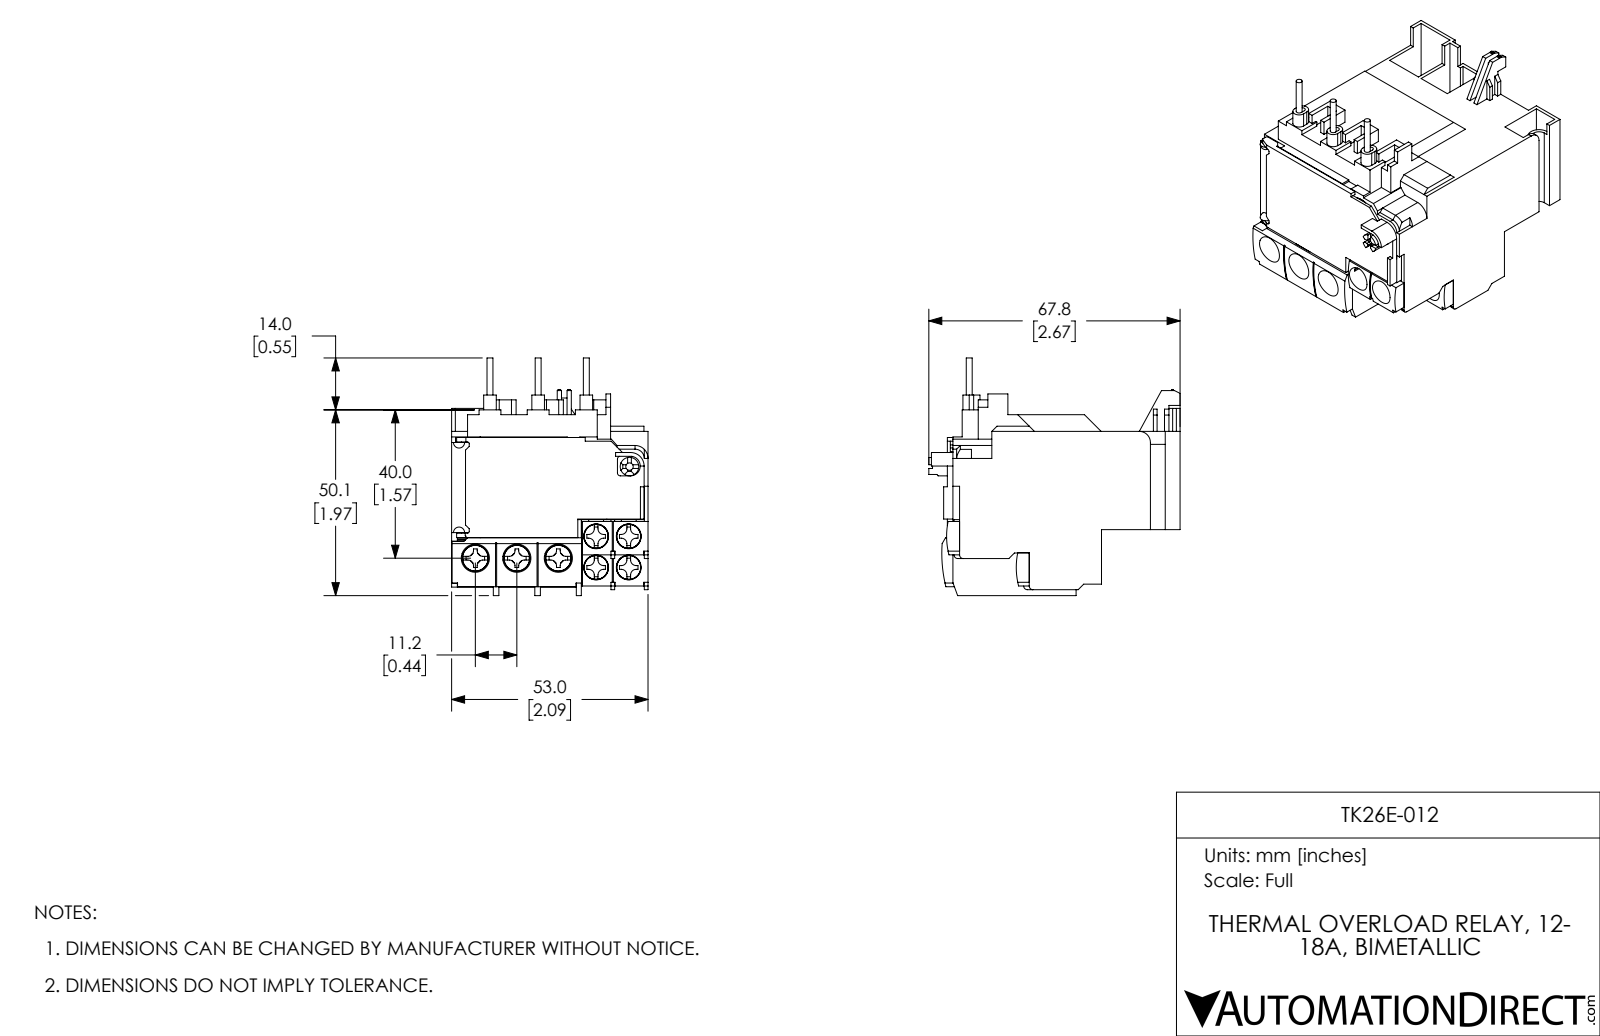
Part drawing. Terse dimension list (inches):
name: TK26E-012
written by: SolidWorks 2017 (AUTOMOTIVE_DESIGN)
unit: in
bodies: 38 solids, 1480 faces (1225 planar, 220 cylindrical, 35 other)
size: 2.669 × 2.524 × 2.087
volume: 6.099 in³; area: 60.15 in²
holes: 4× ⌀0.138, 4× ⌀0.142, 4× ⌀0.264, 3× ⌀0.157, 3× ⌀0.161, 3× ⌀0.299, 1× ⌀0.039, 1× ⌀0.079, 1× ⌀0.197, 1× ⌀0.433
bosses: 4× ⌀0.26, 3× ⌀0.063, 1× ⌀0.236
rounds: 28× R0.059, 8× R0.039, 6× R0.02, 6× R0.067, 5× R0.031, 4× R0.047, 4× R0.171, 3× R0.189
face distances: 0.039, 0.354, 0.059, 0.472, 2.087, 0.079, 0.394, 0.433, 0.343, 0.028
hole spacings: 0.331, 0.346, 0.441, 0.479, 0.376, 0.413, 0.464, 0.74
